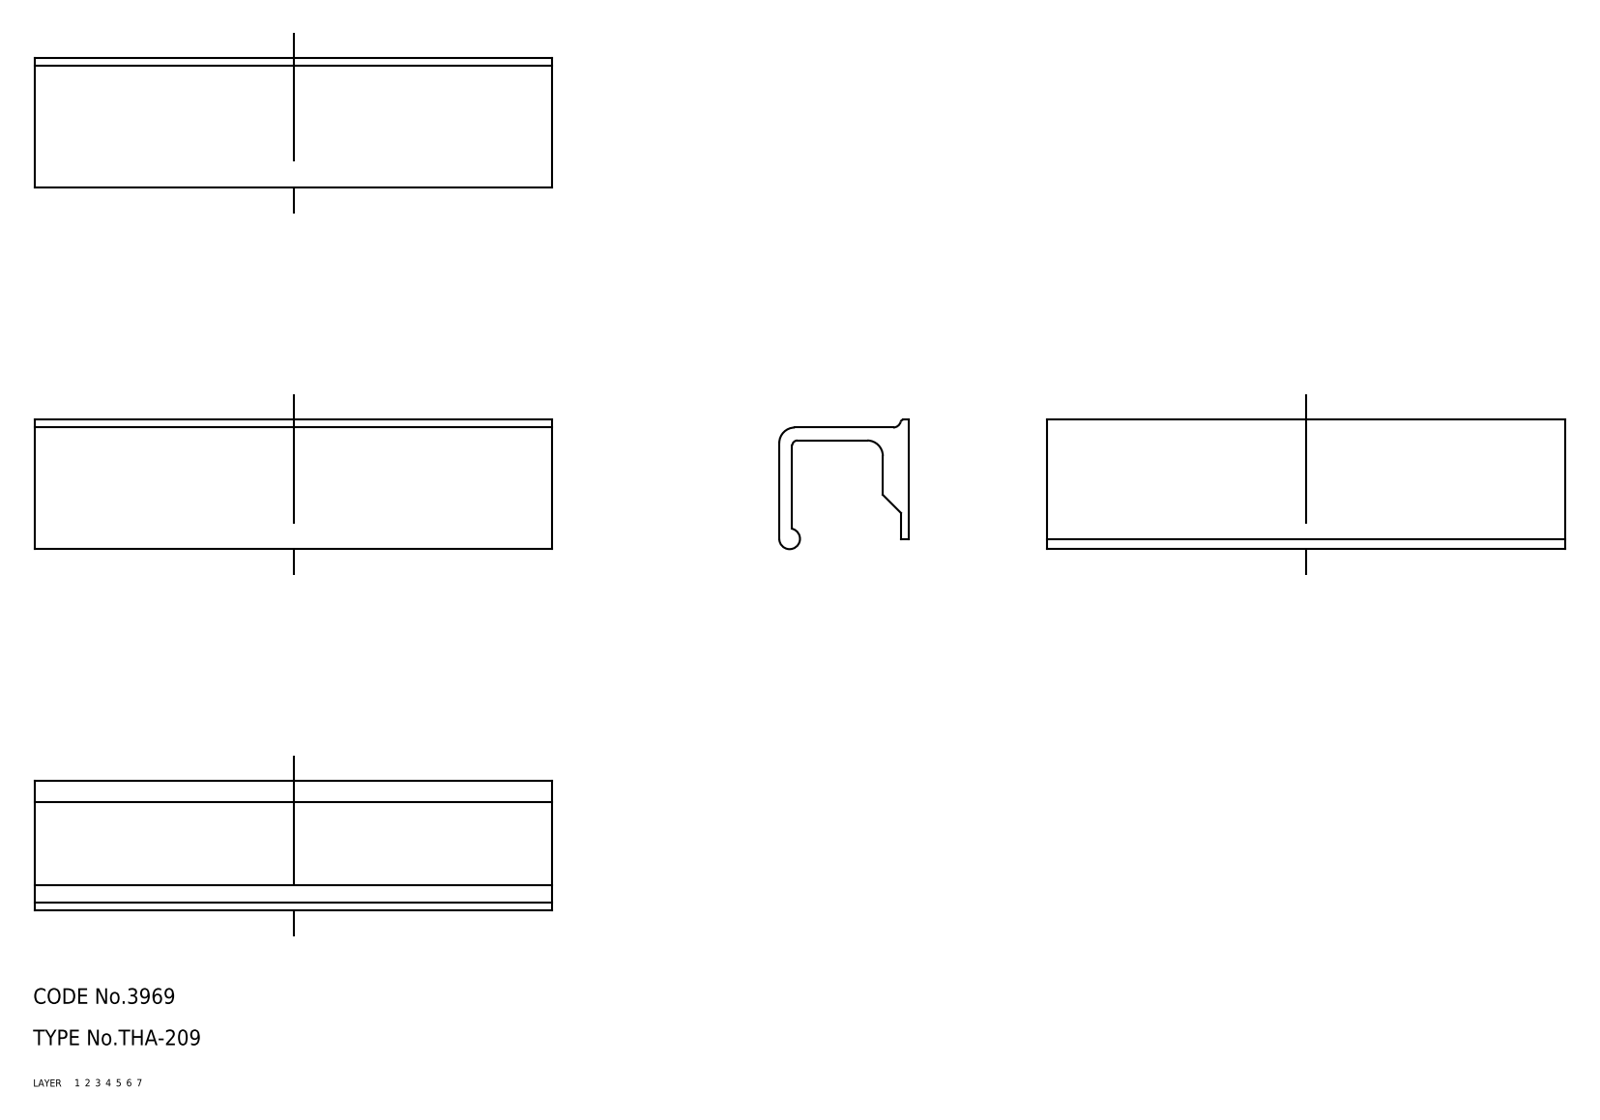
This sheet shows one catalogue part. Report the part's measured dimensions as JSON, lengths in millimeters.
{"part_name": "pull", "step_written_by": "CADfix (AUTOMOTIVE_DESIGN)", "units": "millimeters", "bodies": {"solids": 1, "faces": 18, "planar": 0, "cylindrical": 0, "other": 18}, "overall_size": [100, 25, 25], "volume_mm3": 19273, "surface_area_mm2": 13648}
